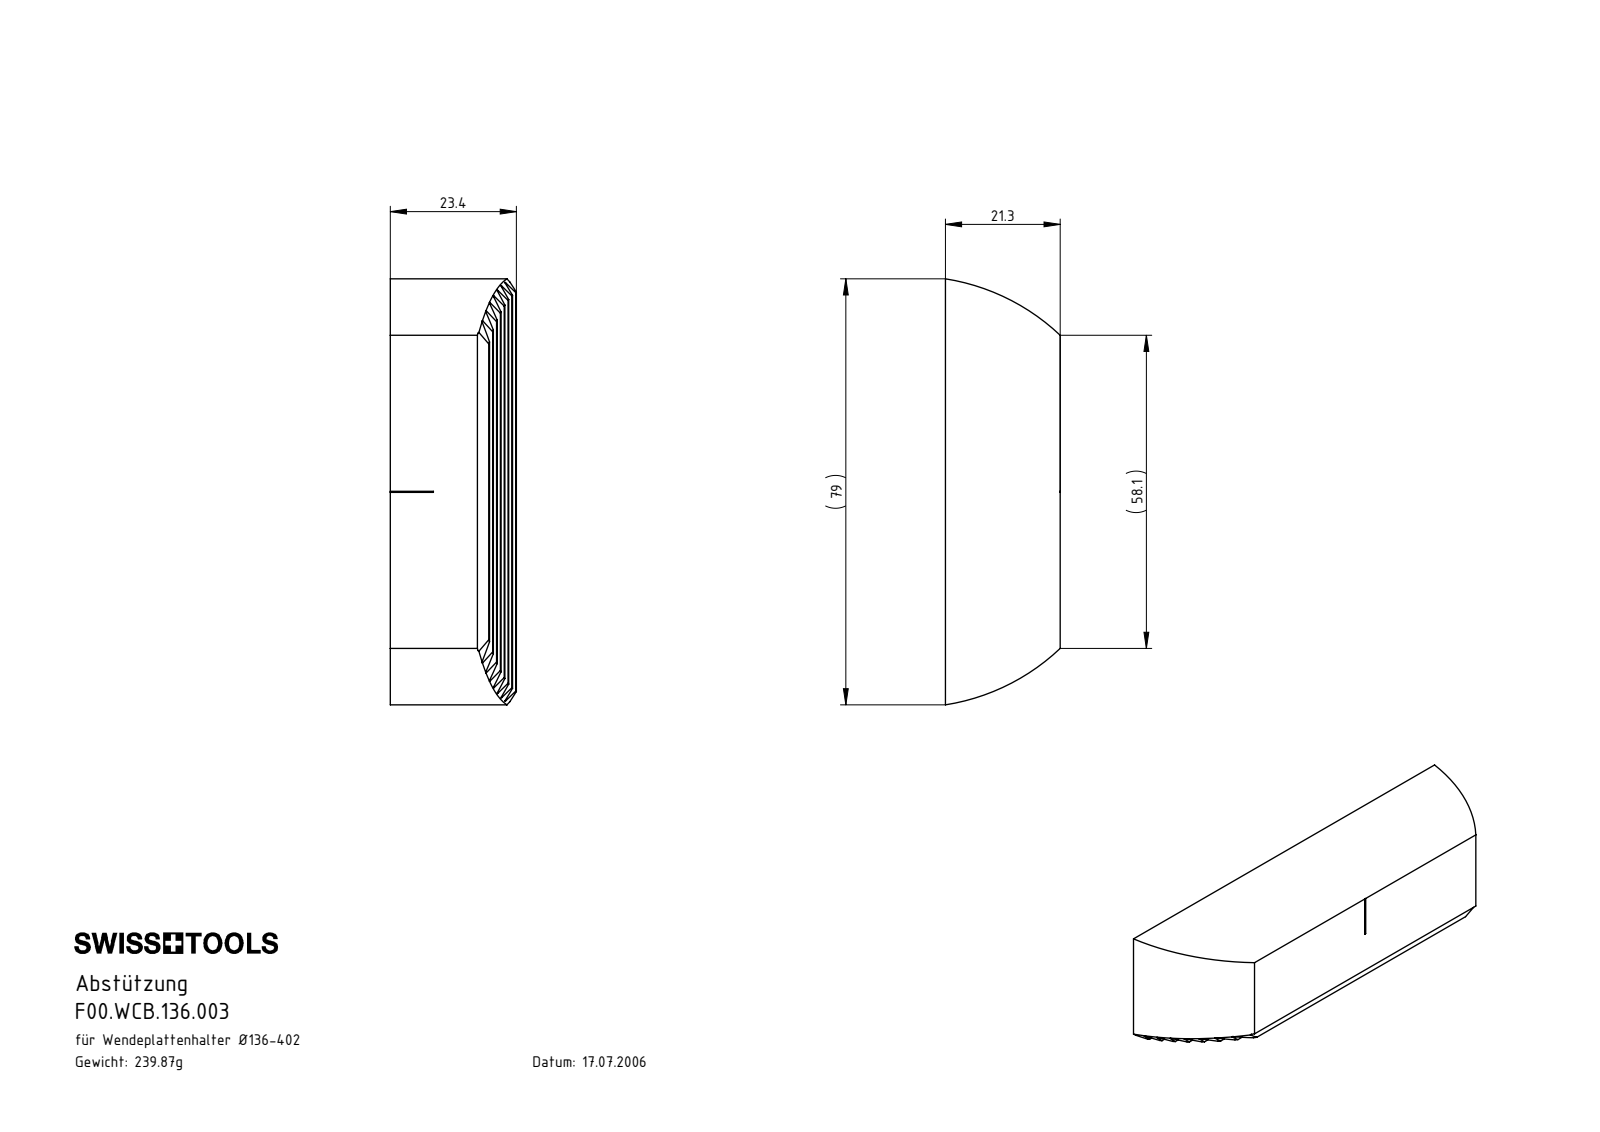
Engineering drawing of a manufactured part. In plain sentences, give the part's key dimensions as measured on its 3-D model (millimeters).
The part is named "F00.WCB.136.003". Its 3-D file was written by "SolidWorks 2017 (AUTOMOTIVE_DESIGN)". It is 1 solid with 12 faces: 8 planar, 2 cylindrical and 2 other. Overall it measures 79.03 by 23.9 by 21.3 millimeters. Its volume is 32 035 cubic millimeters and its surface area 6 978 square millimeters. Partial cylindrical surfaces (rounded edges, fillets, slot ends): 1 of radius 40. The main face-to-face distances are 21.3, 21.28, 8.
